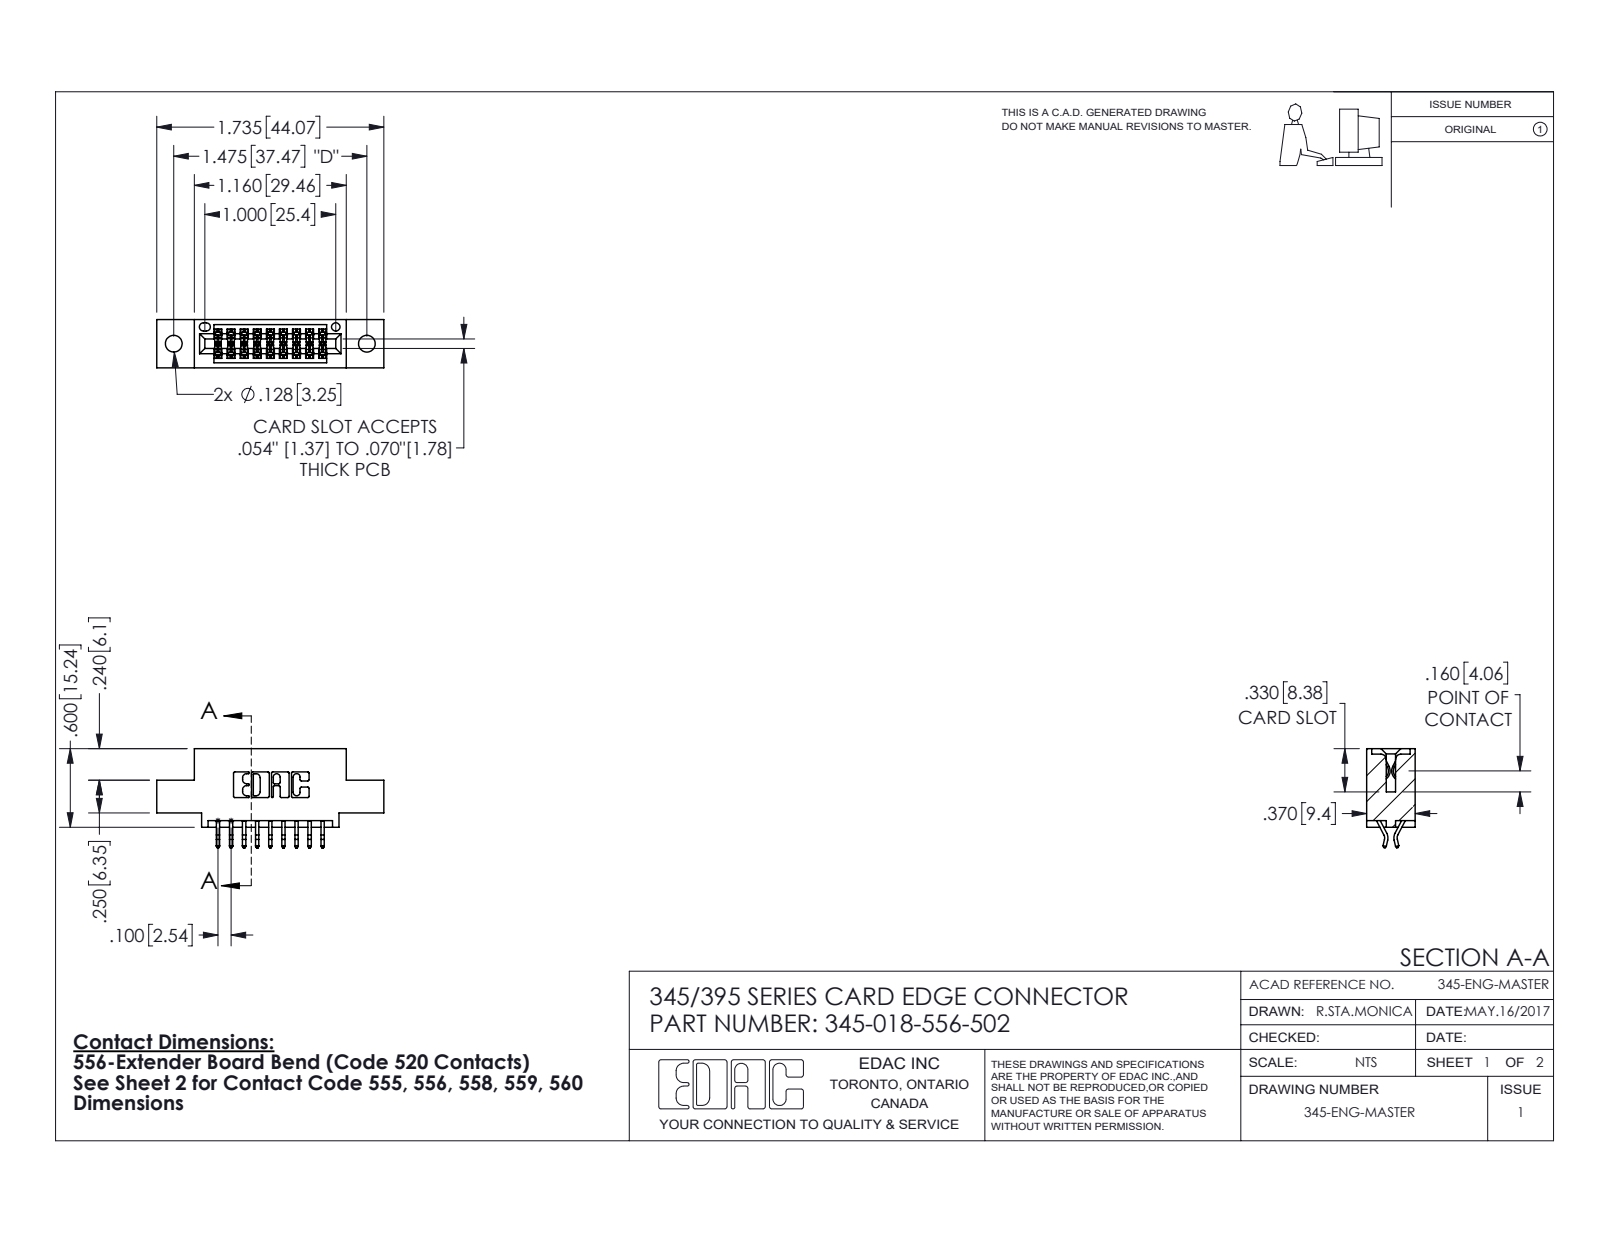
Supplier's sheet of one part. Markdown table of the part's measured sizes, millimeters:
| quantity | value |
| --- | --- |
| part name | 345 Part_0.110 Offset - 0.128 Dia; 345-292-001_556 Tail; 345-018-556-502 |
| STEP written by | SolidWorks 2016 (CONFIG_CONTROL_DESIGN) |
| units | millimeters |
| bodies | 19 solids, 1138 faces (750 planar, 388 cylindrical, 0 other) |
| overall size | 44.1 × 19.2 × 9.4 |
| volume | 3 870 mm³ |
| surface area | 4 877 mm² |
| round holes (diameter × count) | 3.3 × 2, 1.6 × 1 |
| partial cylindrical surfaces (radius × count) | 0.2 × 27, 0.3 × 22, 0.2 × 6, 0.8 × 6, 0.7 × 3, 0.3 × 2, 0.4 × 2, 0.5 × 2 |
| main face-to-face distances | 5.1, 7.6, 1.8, 9.4, 2.5, 0.6, 2.5, 6.9, 5.7, 15.2 |
| hole center spacings | 6.9, 31.6, 37.5 |
